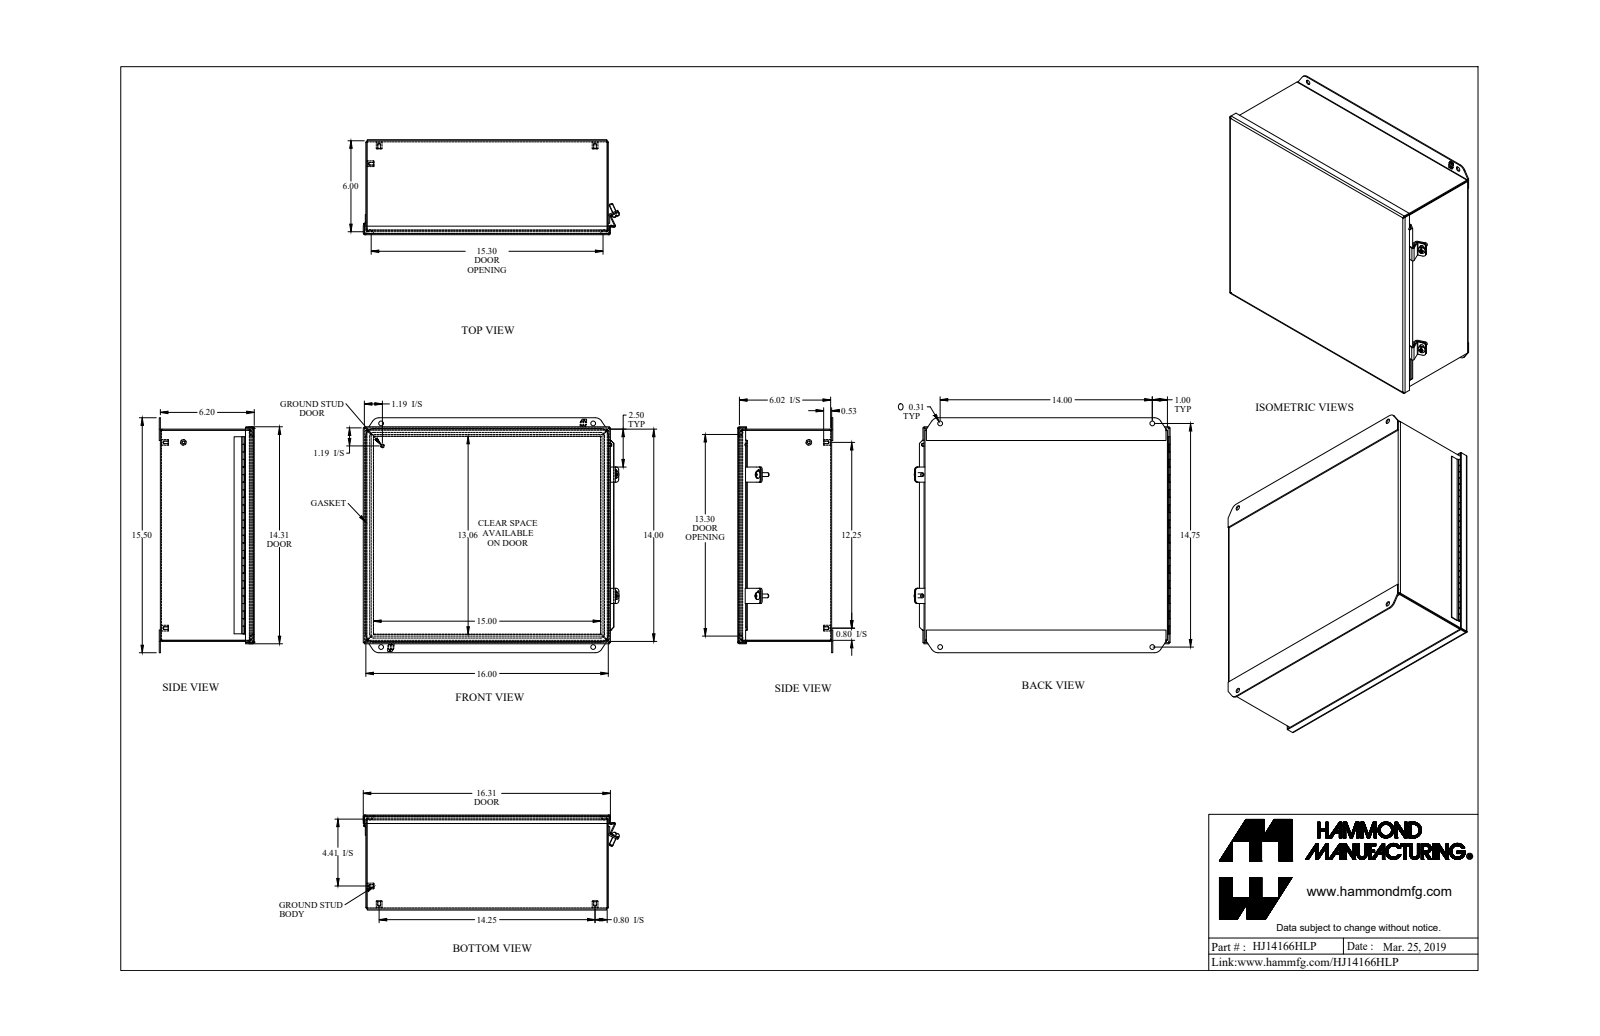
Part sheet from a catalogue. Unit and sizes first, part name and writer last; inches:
Units: inches
Overall size (bounding box): 16.896 × 15.5 × 6.269
Round holes (diameter × count): ⌀0.156 ×5, ⌀0.313 ×4, ⌀0.213 ×2, ⌀0.05 ×1
Round bosses / shafts (diameter × count): ⌀0.375 ×5, ⌀0.25 ×3, ⌀0.48 ×2, ⌀0.188 ×1, ⌀0.1 ×1, ⌀0.045 ×1
Partial cylindrical surfaces — rounded edges, fillets, slot ends (radius × count): R0.25 ×16, R0.036 ×13, R0.108 ×13, R0.01 ×4, R0.029 ×4, R0.086 ×4, R0.141 ×4, R0.188 ×4
Main face-to-face distances: 0.072, 6.125, 6.197, 6.053, 13.928, 15.928, 14, 13.856, 15.856, 16
Hole centre spacings: 1.257, 13.5, 14.18, 19.539, 12.25, 14, 14.25, 14.75
Volume: 71.78 in³ · Surface area: 2 009 in²
Bodies: 20 solids, 809 faces (430 planar, 251 cylindrical, 128 other)
Part name (STEP PRODUCT): HJ14166HLP
STEP written by: SolidWorks 2018 (AUTOMOTIVE_DESIGN)
